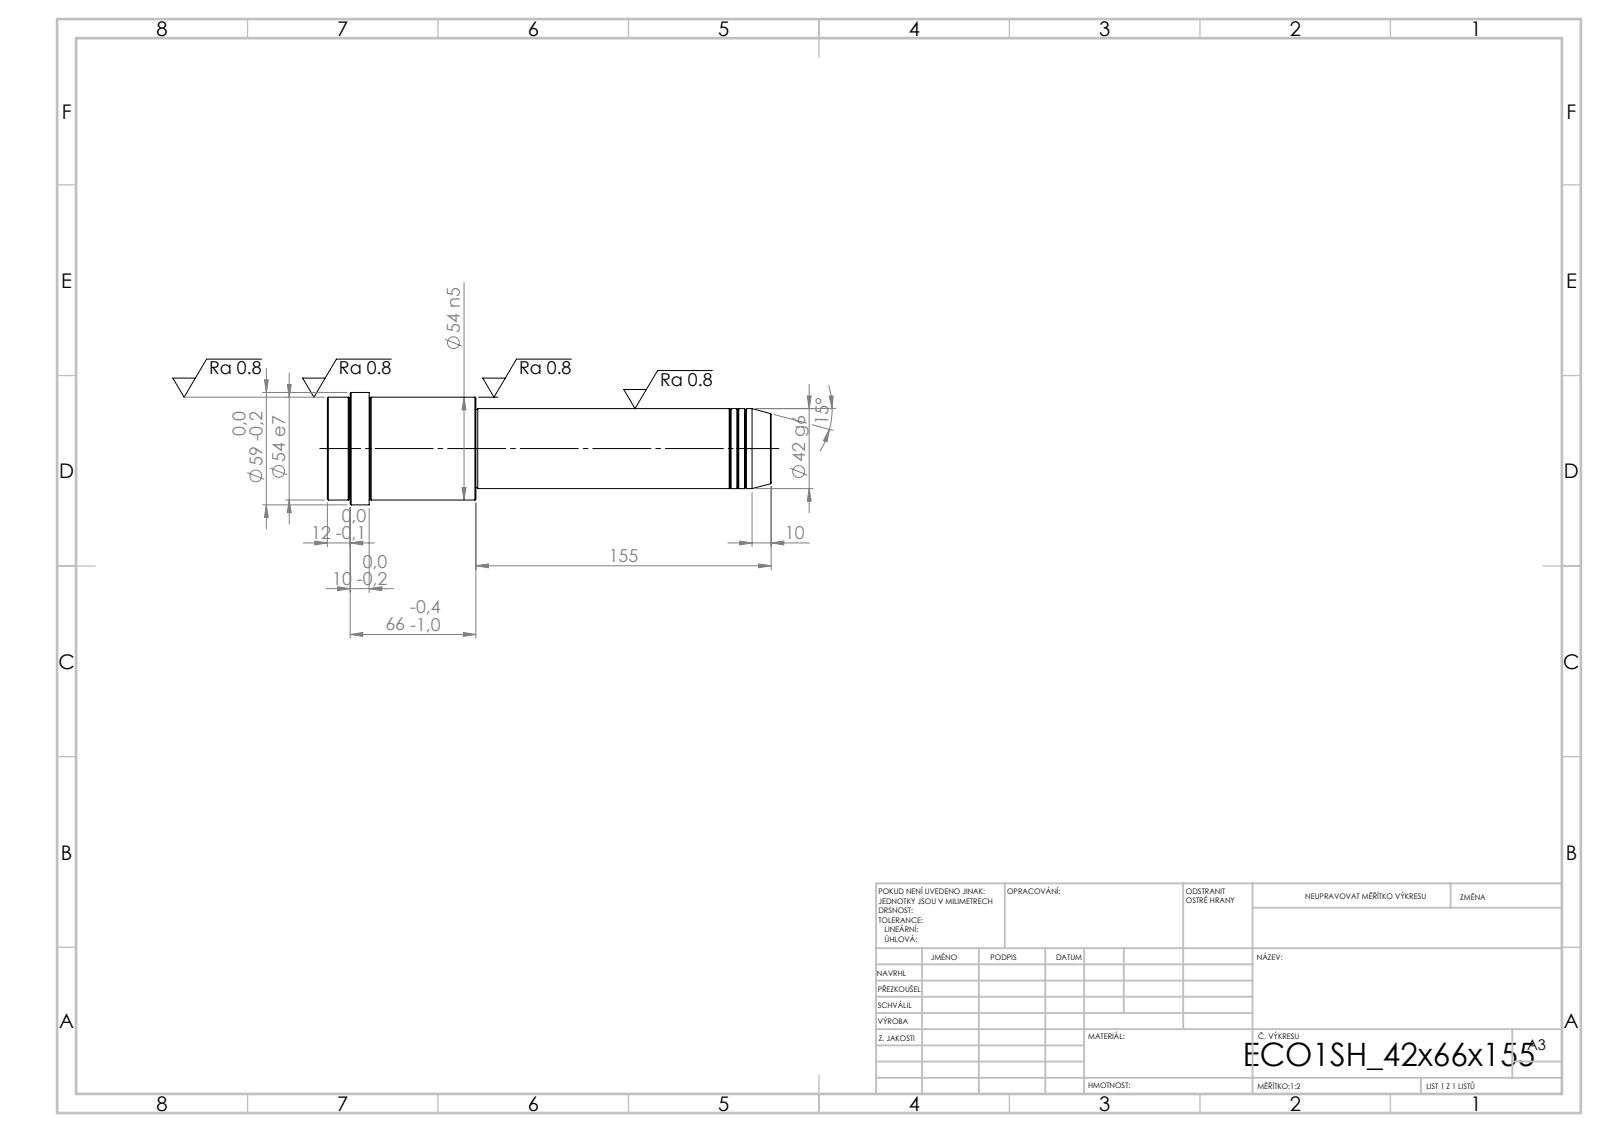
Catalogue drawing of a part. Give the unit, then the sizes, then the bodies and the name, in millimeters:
Units: millimetres
Overall size (bounding box): 233 × 59 × 59
Round bosses / shafts (diameter × count): ⌀59 ×1, ⌀54 ×1, ⌀42 ×1, ⌀41 ×1
Main face-to-face distances: 233, 155, 78, 211, 56, 22, 221, 66, 10, 12
Volume: 395 706 mm³ · Surface area: 39 301 mm²
Bodies: 1 solid, 52 faces (6 planar, 16 cylindrical, 30 other)
STEP written by: SolidWorks 2019 (CONFIG_CONTROL_DESIGN)
